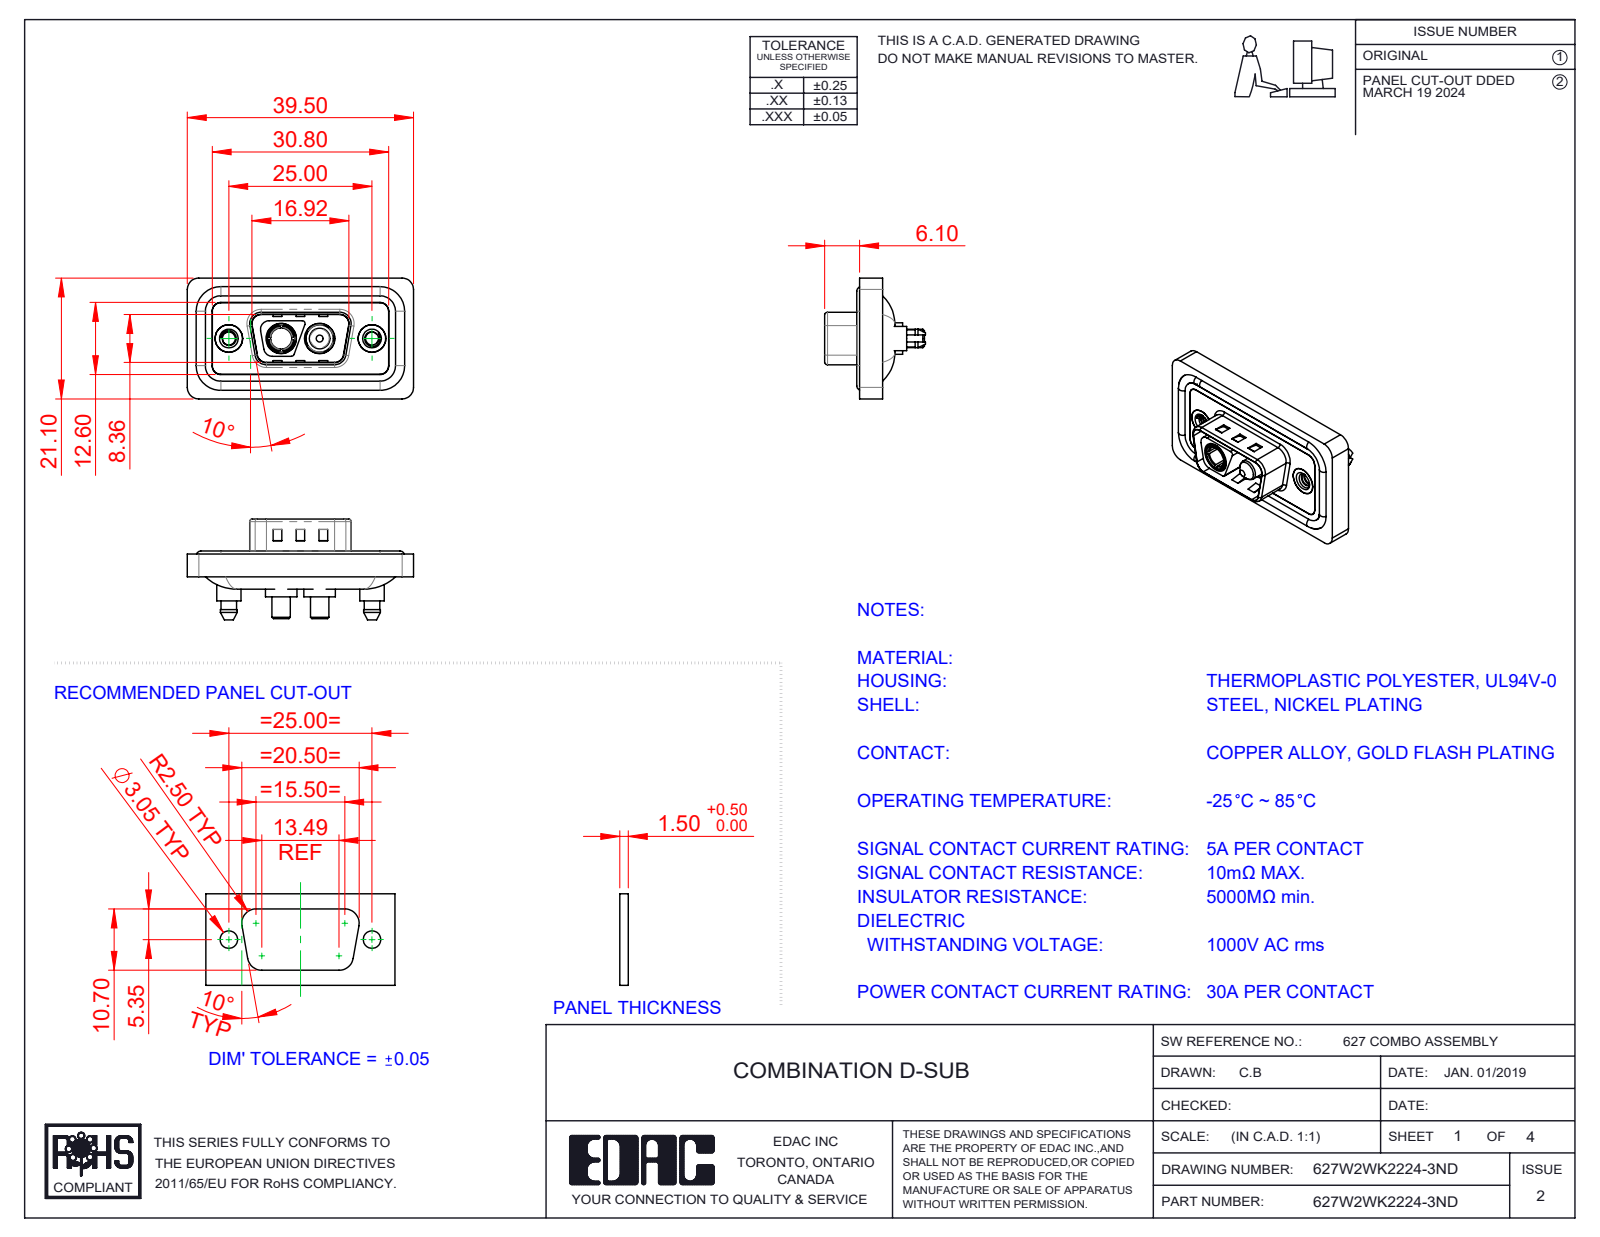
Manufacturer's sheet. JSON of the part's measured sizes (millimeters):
{"part_name": "627Combo Threaded Boardlock_5; 627Combo Shell Rear_09 Contacts; Power Pin_30A S; Power Socket_30A S (+5 more)", "step_written_by": "SolidWorks 2023 (CONFIG_CONTROL_DESIGN)", "units": "millimeters", "bodies": {"solids": 11, "faces": 592, "planar": 205, "cylindrical": 267, "other": 120}, "overall_size": [39.5, 21.1, 17.6], "volume_mm3": 4703, "surface_area_mm2": 7688, "round_holes": [[2.26, 2], [4, 2], [4.8, 2], [4.85, 2], [5, 2], [5.3, 2], [3.7, 1]], "round_bosses_or_shafts": [[1.6, 4], [5.5, 2], [5.4, 2], [5.2, 2], [4.9, 2], [4.75, 2], [4.25, 2], [3.75, 2]], "partial_cylinders_radius": [[1.5, 26], [2, 18], [0.5, 10], [1.6, 10], [0.25, 4], [0.6, 4], [0.65, 4], [0.9, 4]], "face_to_face_distances": [0.4, 1.1, 2.9, 3.1, 0.5, 1.6, 1.5, 4, 1.8, 3.2], "hole_center_spacings": [9.14, 15.86, 6.72, 25]}
